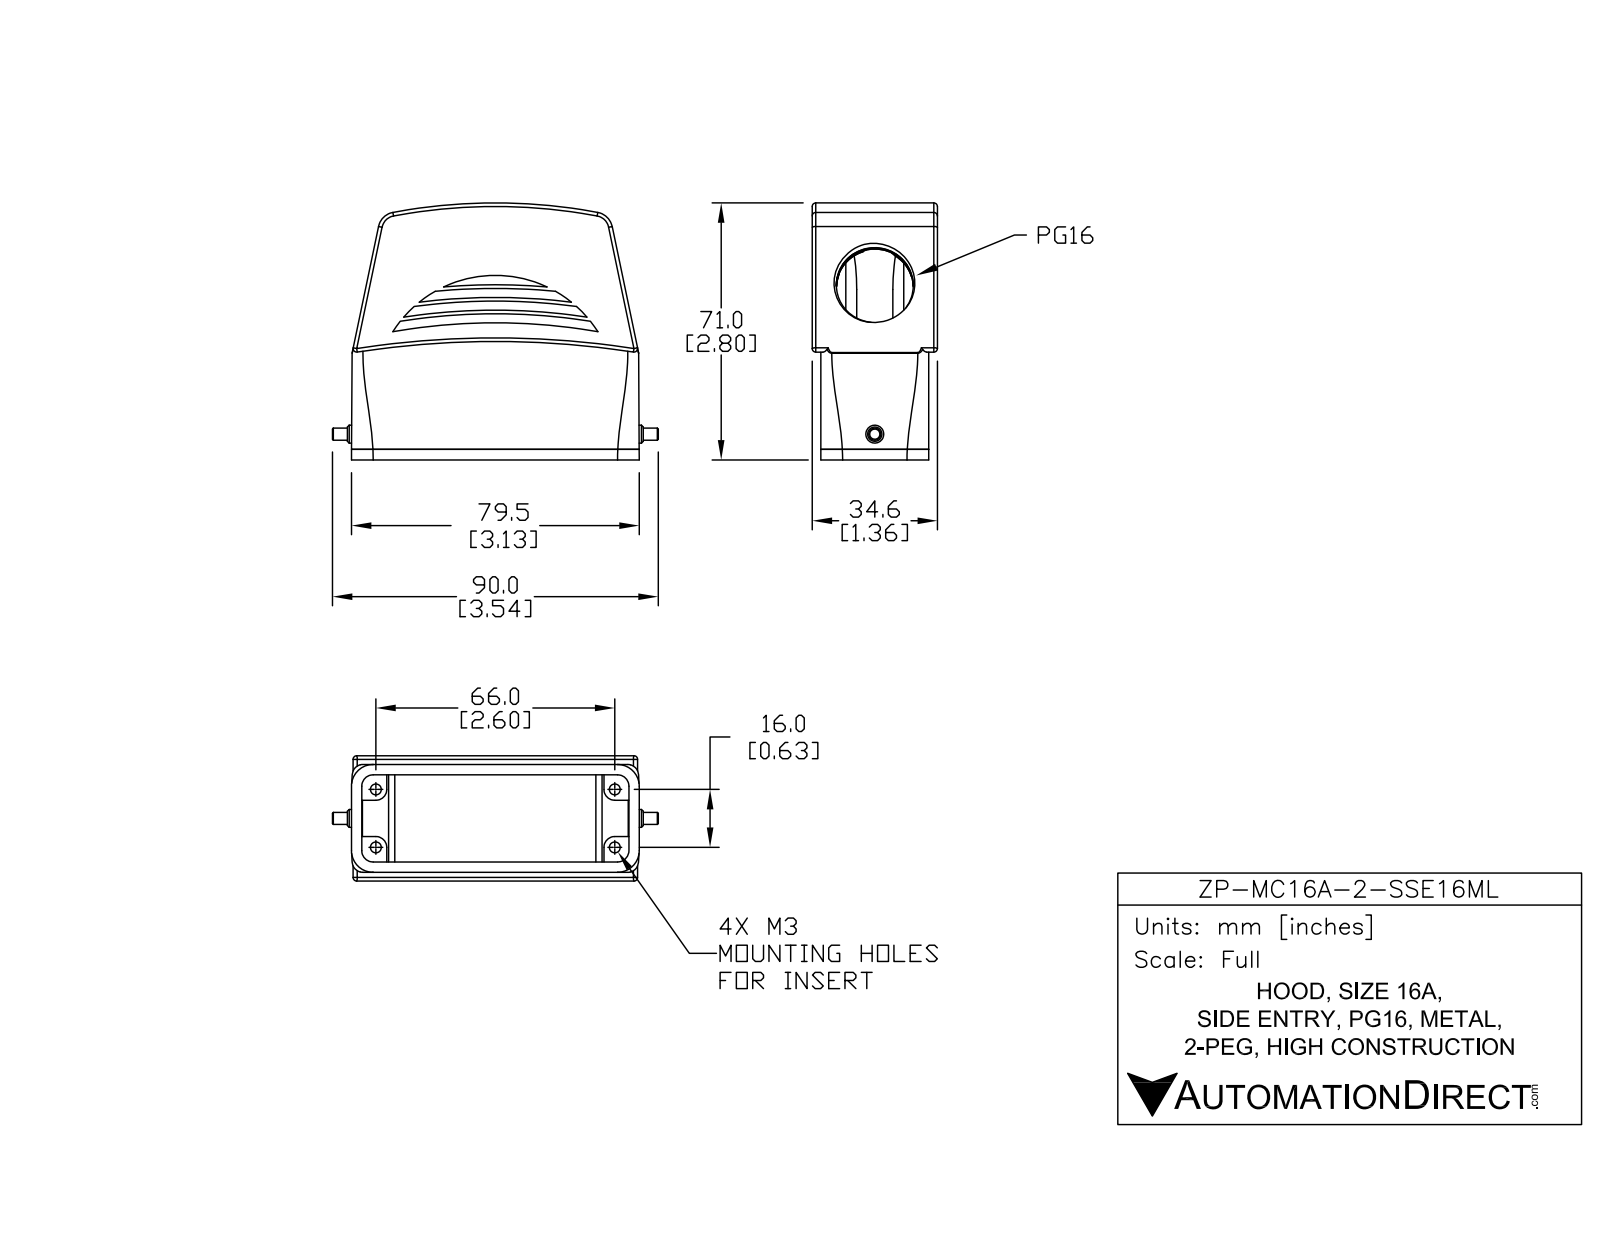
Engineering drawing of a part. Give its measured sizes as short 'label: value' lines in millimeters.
name: ZP-MC16A-2-SSE16ML
written by: SolidWorks 2014 (AUTOMOTIVE_DESIGN)
unit: mm
bodies: 2 solids, 181 faces (54 planar, 78 cylindrical, 49 other)
size: 90 × 71 × 34.6
volume: 59 407 mm³; area: 32 971 mm²
holes: 4× ⌀3, 1× ⌀21.25
bosses: 1× ⌀4.95, 1× ⌀3.33
rounds: 9× R1, 4× R3, 2× R2.15, 2× R5, 1× R33.56, 1× R150.6, 1× R153.45, 1× R164.53
face distances: 2.85, 26.93, 24.08, 2.41, 5.26, 29.34, 32.19, 29.78, 34.6, 34.35
hole spacings: 16, 66, 67.91
